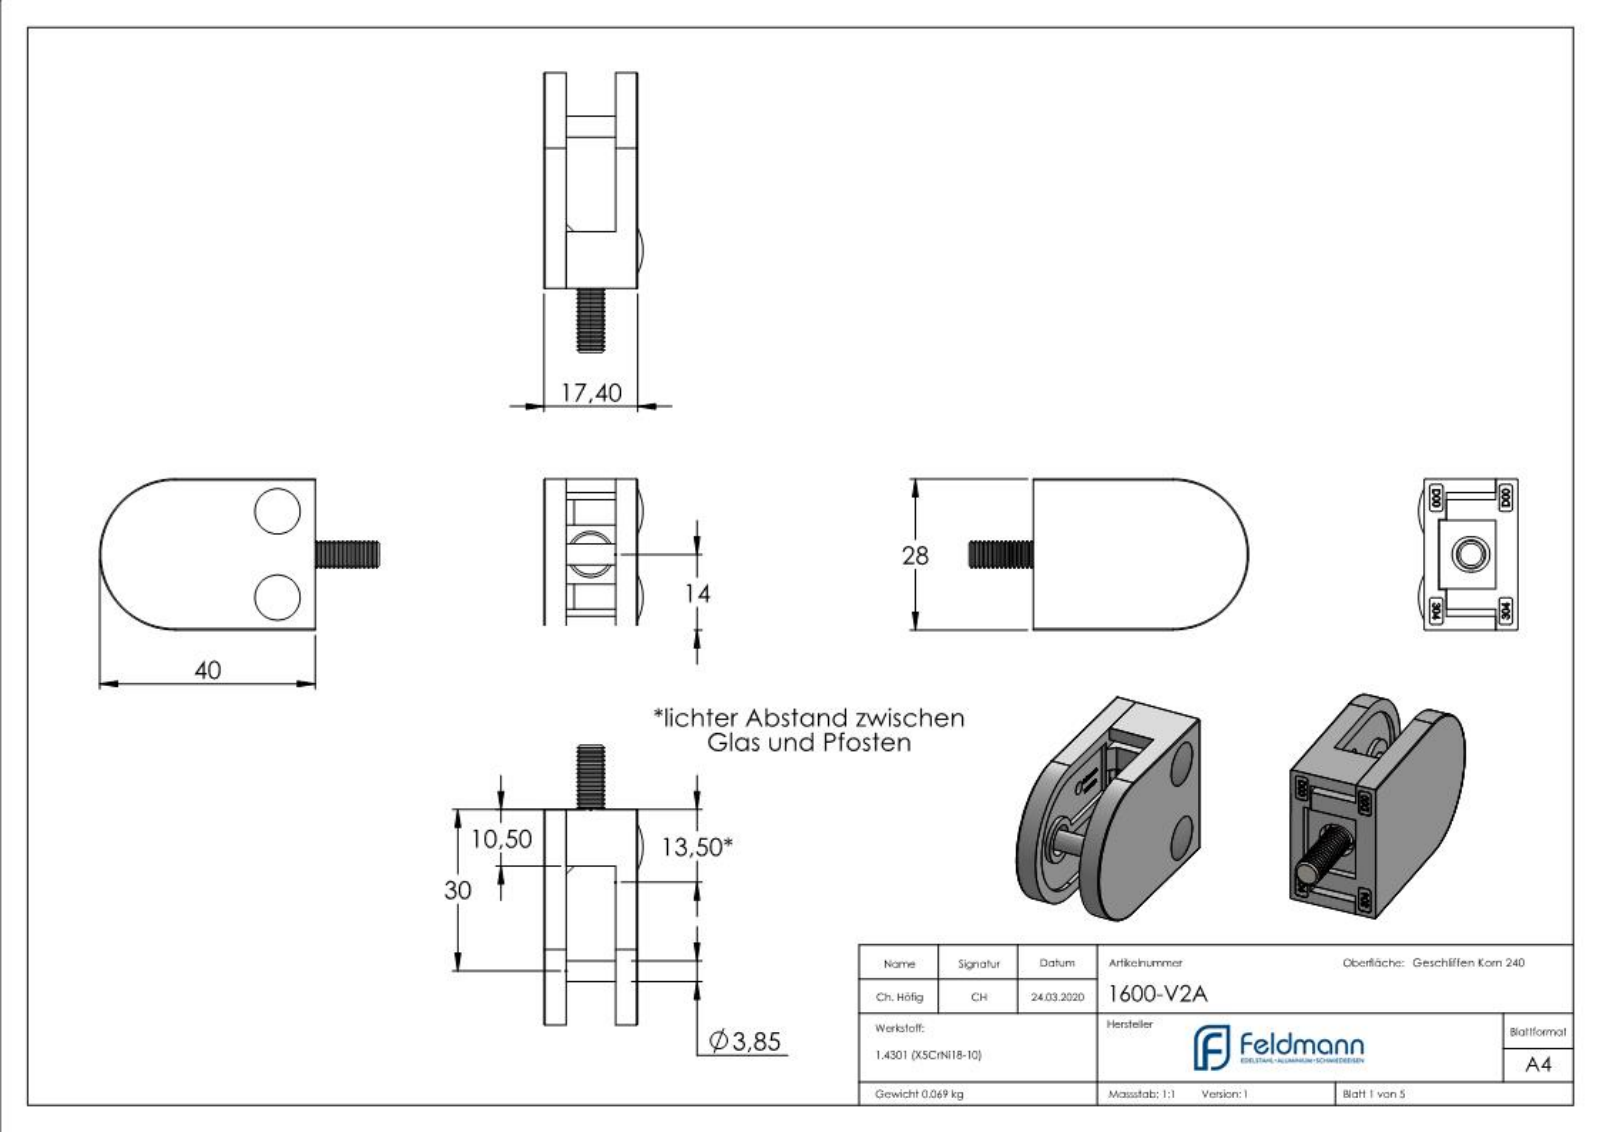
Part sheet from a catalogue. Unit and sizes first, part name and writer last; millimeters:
Units: millimetres
Overall size (bounding box): 51.9 × 28 × 18.4
Round holes (diameter × count): ⌀1 ×2, ⌀2.5 ×2, ⌀3.3 ×2, ⌀4.15 ×2, ⌀8.2 ×2, ⌀3.9 ×1, ⌀6 ×1
Round bosses / shafts (diameter × count): ⌀7.64 ×2, ⌀4 ×2, ⌀2.5 ×2, ⌀8.8 ×1, ⌀8.5 ×1, ⌀5 ×1, ⌀3.85 ×1
Partial cylindrical surfaces — rounded edges, fillets, slot ends (radius × count): R0.5 ×20, R0.2 ×4, R3.25 ×2, R11.6 ×1, R14 ×1
Main face-to-face distances: 17.4, 4.1, 3.2, 14.2, 13.3, 0.9, 10.1, 11, 9.2, 2.5
Hole centre spacings: 10.99, 14.1, 20.01, 24.35, 12.6, 16
Volume: 9 512 mm³ · Surface area: 8 730 mm²
Bodies: 8 solids, 1193 faces (537 planar, 160 cylindrical, 496 other)
Part name (STEP PRODUCT): 1600-V2A; socket countersunk head screw_din_DIN 7991 - M4 x 10 --- 10S; 16-Stift_16-Stift; 16xx-XXX Teil2_1600-V2A (+3 more)
STEP written by: SolidWorks 2015 (CONFIG_CONTROL_DESIGN)
